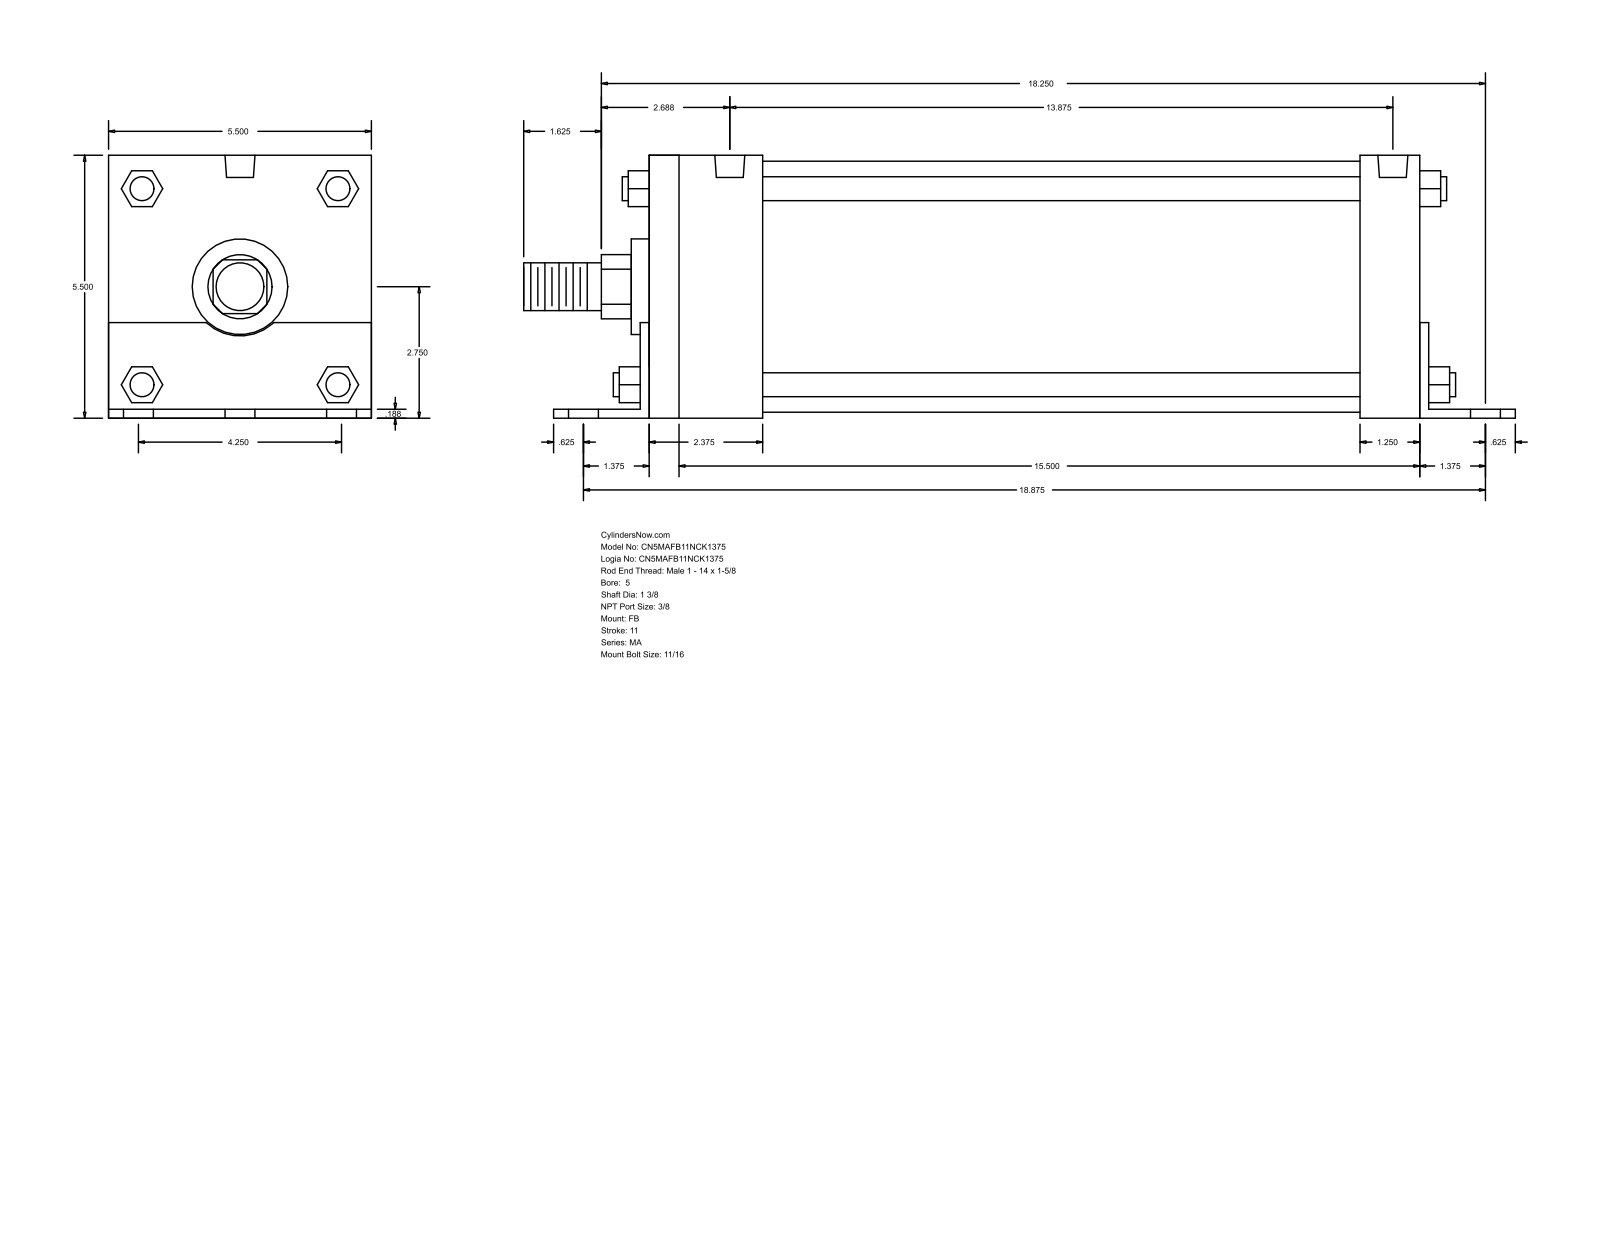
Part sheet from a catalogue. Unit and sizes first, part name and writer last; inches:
Units: inches
Overall size (bounding box): 20.75 × 5.502 × 5.5
Round holes (diameter × count): ⌀0.687 ×6, ⌀0.437 ×4, ⌀0.627 ×2
Round bosses / shafts (diameter × count): ⌀0.5 ×4, ⌀5.25 ×1, ⌀2 ×1, ⌀1.375 ×1, ⌀1 ×1
Partial cylindrical surfaces — rounded edges, fillets, slot ends (radius × count): R0.672 ×1, R1.03 ×1
Main face-to-face distances: 5.5, 0.187, 5.502, 16.313, 0.185, 5.315, 16.125, 16.5, 1.25, 1.437
Hole centre spacings: 2.125, 18.994, 18.875, 2.876, 3.005, 3.728, 3.883, 4.25
Bodies: 0 solids, 140 faces (105 planar, 35 cylindrical, 0 other)
Part name (STEP PRODUCT): MA_FB__0500_1.375
STEP written by: GSSL Pune (CONFIG_CONTROL_DESIGN)
